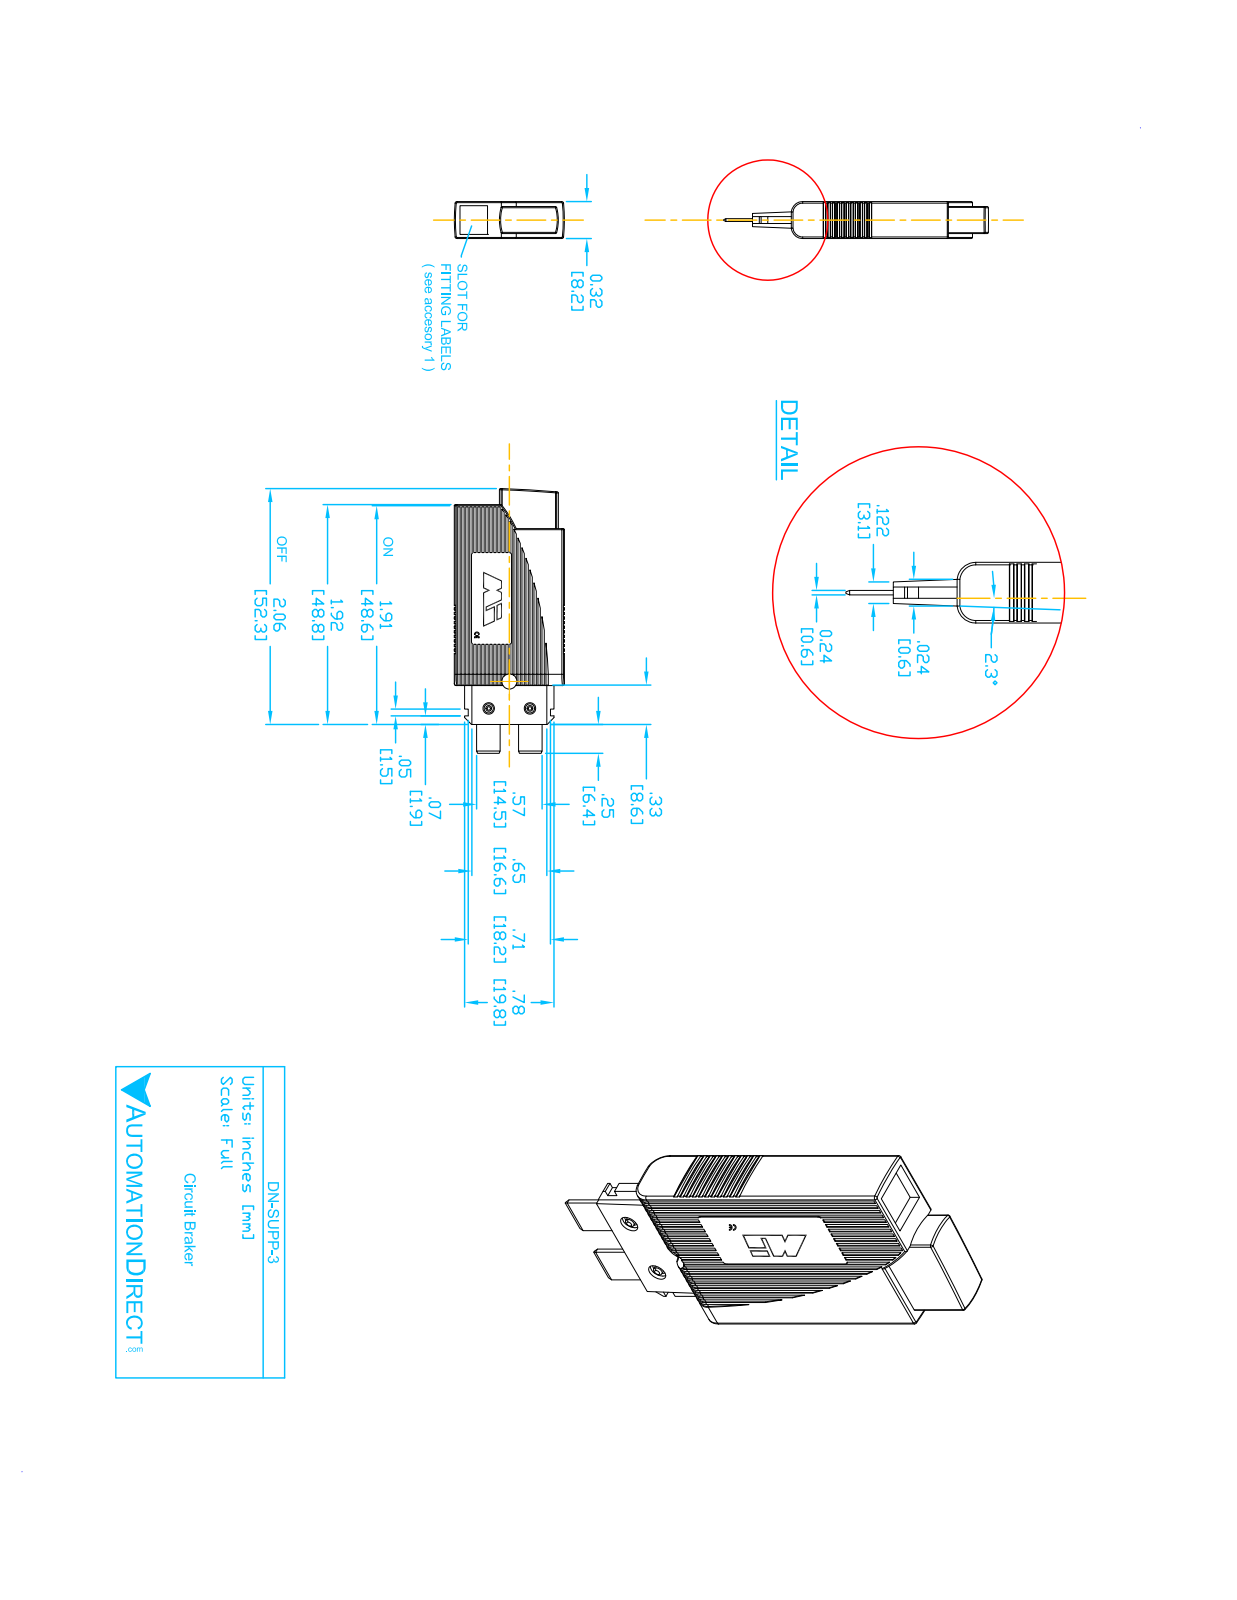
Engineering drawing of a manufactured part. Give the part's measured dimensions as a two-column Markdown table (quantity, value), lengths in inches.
| quantity | value |
| --- | --- |
| part name | DN-SUPP-3 |
| STEP written by | SolidWorks 2017 (AUTOMOTIVE_DESIGN) |
| units | inches |
| bodies | 1 solid, 95 faces (47 planar, 28 cylindrical, 20 other) |
| overall size | 2.18 × 0.961 × 0.323 |
| volume | 0.505 in³ |
| surface area | 5.231 in² |
| partial cylindrical surfaces (radius × count) | 0.012 × 21, 0.157 × 2, 2.165 × 1, 2.331 × 1, 2.362 × 1 |
| main face-to-face distances | 0.323, 0.961, 0.15, 0.173, 0.031, 0.291, 0.118, 0.142, 0.024, 0.14 |
